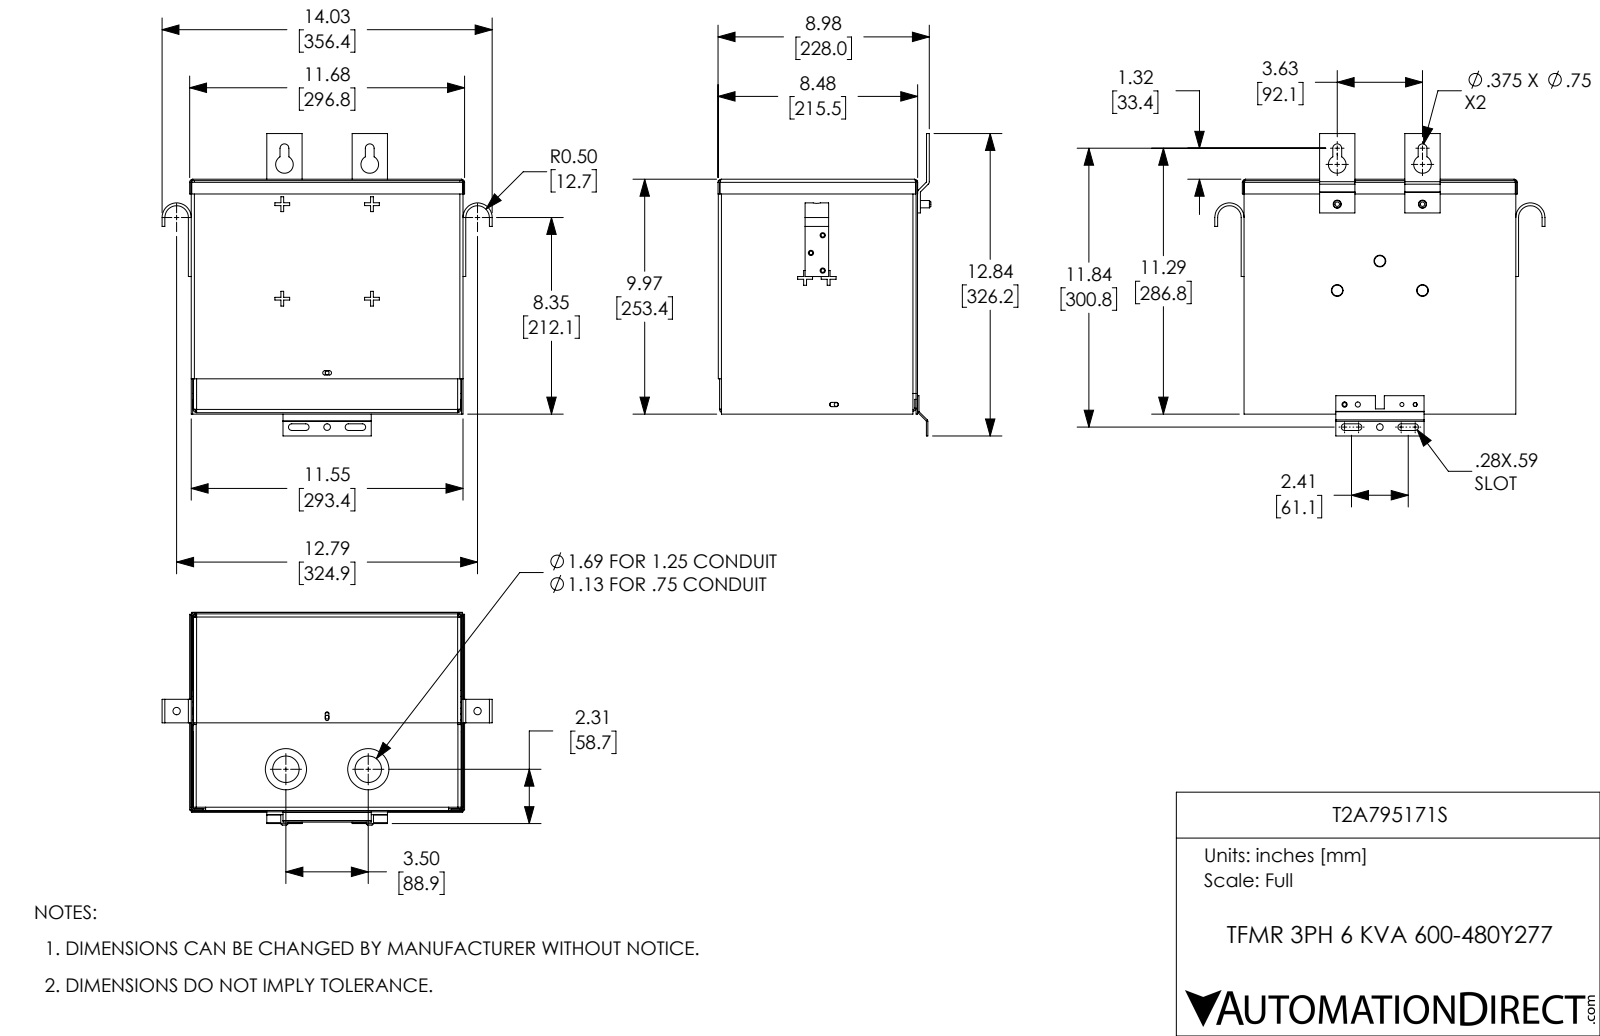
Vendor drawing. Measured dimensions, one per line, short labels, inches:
name: T2A795171S
written by: SolidWorks 2017 (AUTOMOTIVE_DESIGN)
unit: in
bodies: 12 solids, 602 faces (392 planar, 138 cylindrical, 72 other)
size: 14.03 × 12.844 × 9.042
volume: 40.81 in³; area: 1 348 in²
holes: 5× ⌀0.16, 2× ⌀0.172, 2× ⌀0.219, 2× ⌀0.281, 2× ⌀0.313, 2× ⌀0.344, 2× ⌀0.75, 2× ⌀1.75, 1× ⌀0.173, 1× ⌀0.187, 1× ⌀1.125, 1× ⌀1.125
bosses: 2× ⌀1.87, 2× ⌀1.245, 2× ⌀0.312
rounds: 16× R0.075, 16× R0.135, 8× R0.094, 4× R0.141, 2× R0.02, 2× R0.03, 2× R0.078, 2× R0.08
face distances: 0.06, 8.41, 8.35, 9.855, 8.47, 0.059, 11.491, 0.065, 9.79, 11.55
hole spacings: 0.563, 1.342, 1.638, 1.687, 1.781, 2.014, 2.437, 2.821
